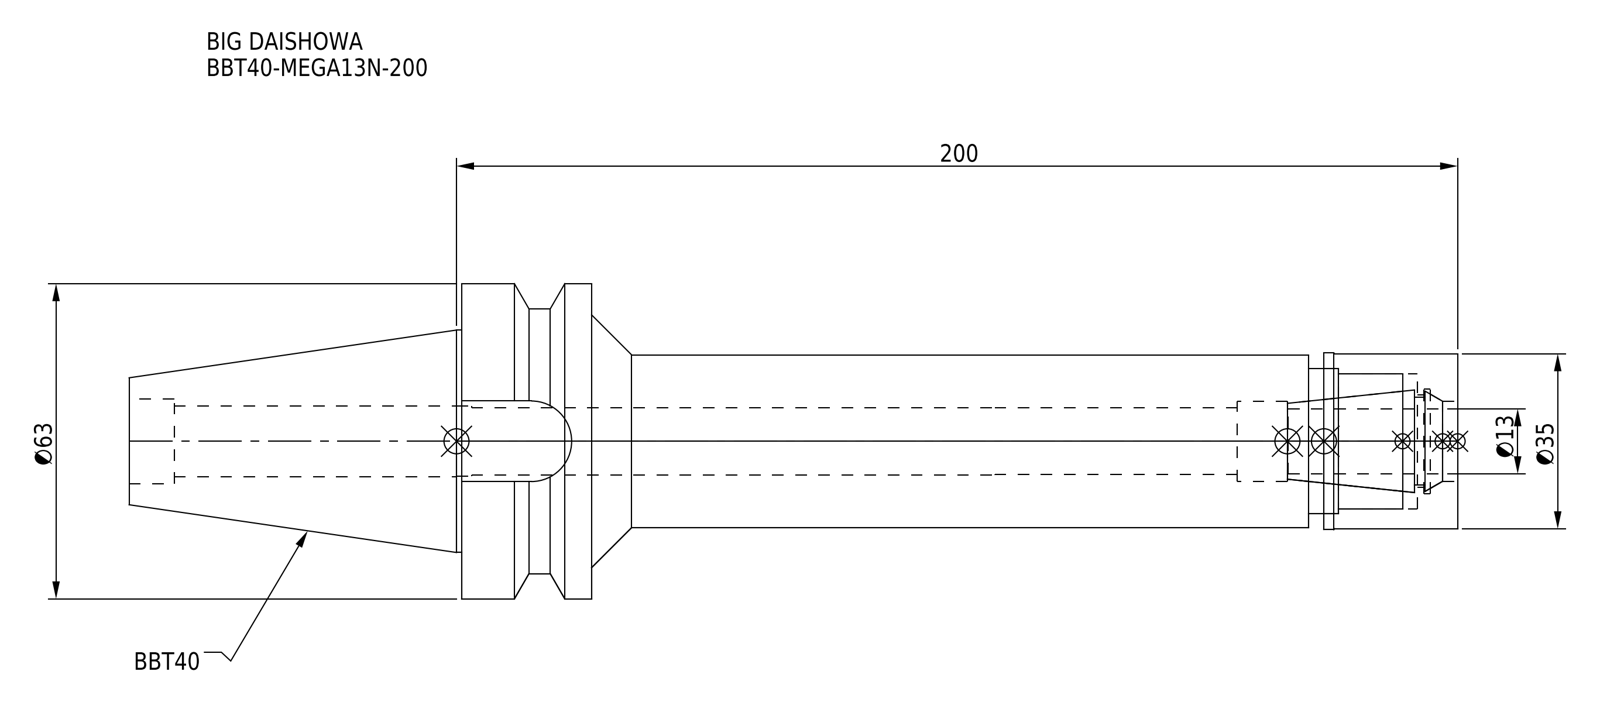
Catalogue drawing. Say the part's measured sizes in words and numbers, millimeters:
The part is named "BBT40-MEGA13N-200-130-FreeParts; DXF_TEMP_ASSY_ASM_4_ASM.stp; BBT40-MEGA13N-200; BBT40-MEGA13N-200_1.stp (+3 more)". Its 3-D file was written by "SolidWorks 2019 (CONFIG_CONTROL_DESIGN)". It is 2 solids with 80 faces: 24 planar, 42 cylindrical and 14 other. Overall it measures 265.4 by 63 by 63 millimeters. Its volume is 256 772 cubic millimeters and its surface area 53 165 square millimeters. Round holes: 1 of diameter 13.3, 1 of diameter 13.5, 1 of diameter 14, 1 of diameter 14.2, 1 of diameter 16, 1 of diameter 17, 1 of diameter 18.5, 1 of diameter 21, 1 of diameter 27, 1 of diameter 29. Round bosses or shafts: 1 of diameter 63, 1 of diameter 53, 1 of diameter 44.45, 1 of diameter 35.3, 1 of diameter 35, 1 of diameter 34.5. Partial cylindrical surfaces (rounded edges, fillets, slot ends): 1 of radius 8.05. The main face-to-face distances are 26, 173, 199, 45, 165, 26.7, 146.3, 172.3, 8, 18.7.
